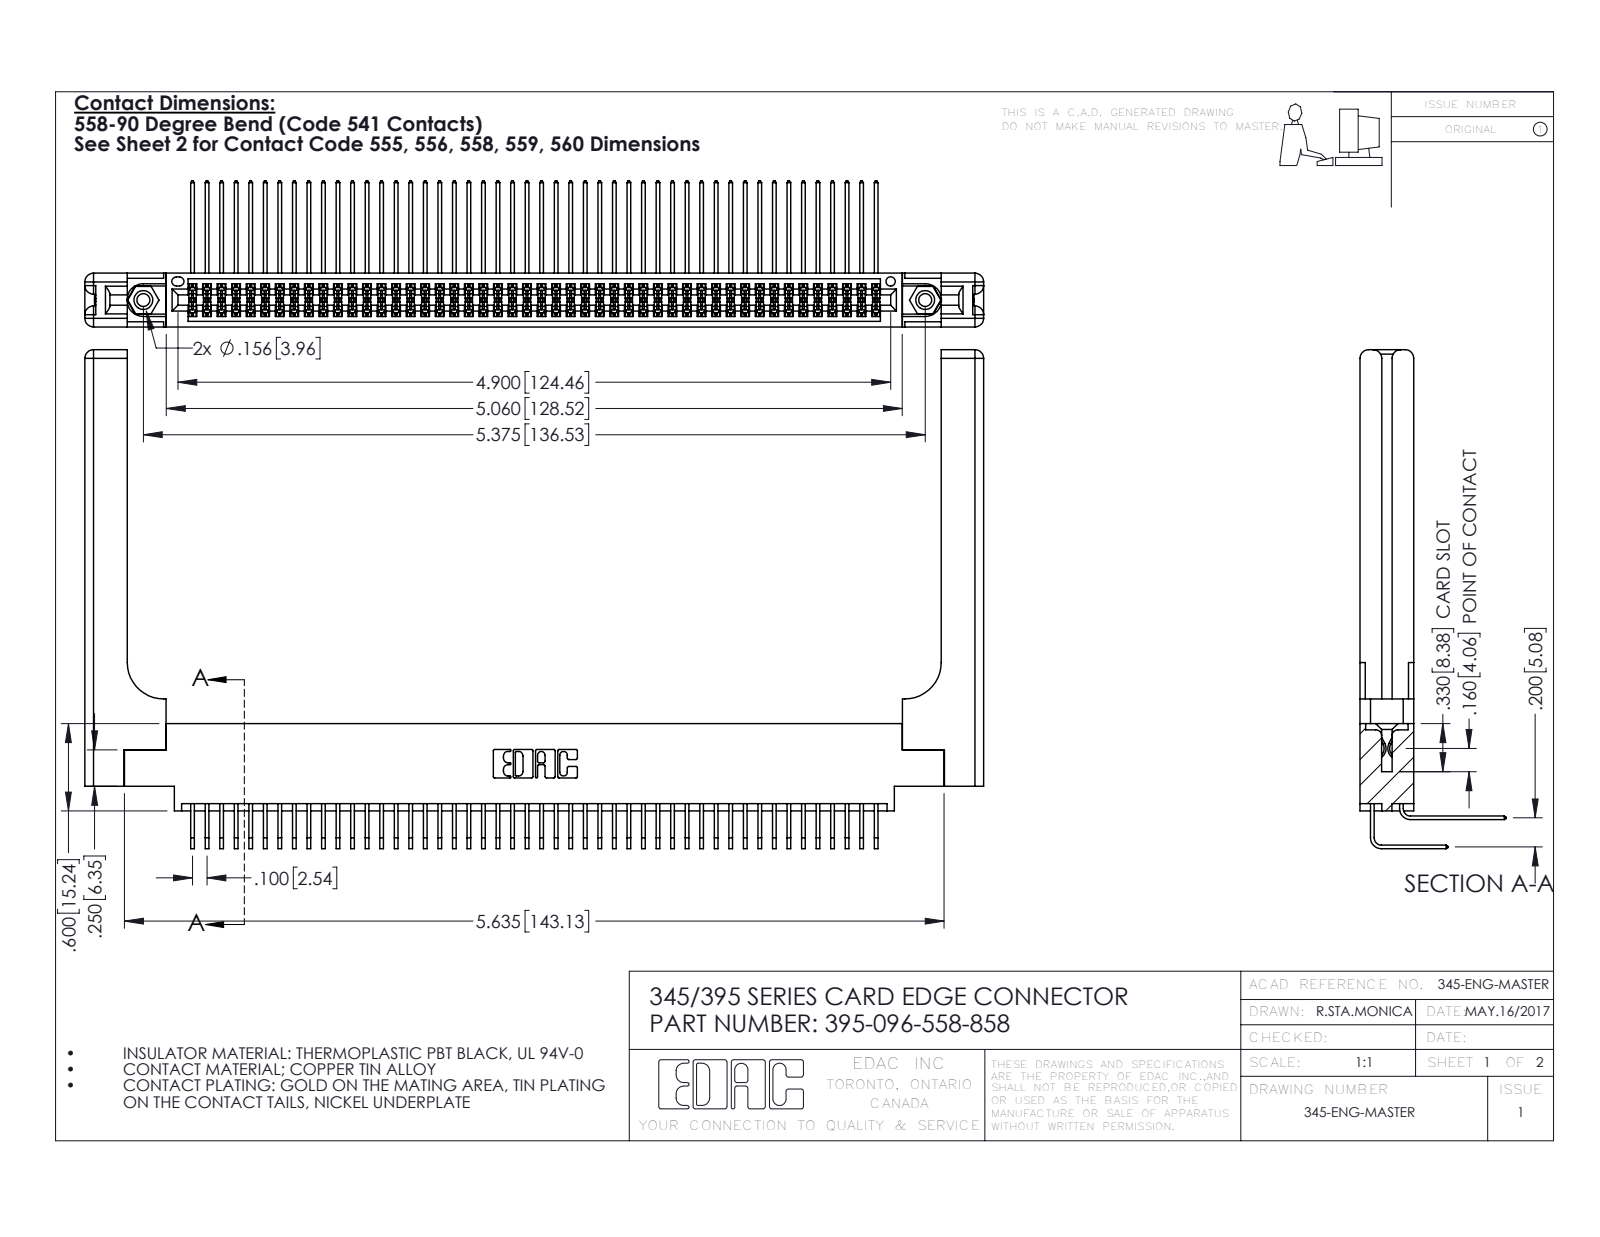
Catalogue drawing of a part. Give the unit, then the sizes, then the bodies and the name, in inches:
Units: inches
Overall size (bounding box): 6.179 × 3.429 × 1.005
Round holes (diameter × count): ⌀0.089 ×2, ⌀0.125 ×2, ⌀0.156 ×2, ⌀0.064 ×1
Round bosses / shafts (diameter × count): ⌀0.155 ×2
Partial cylindrical surfaces — rounded edges, fillets, slot ends (radius × count): R0.006 ×145, R0.01 ×22, R0.06 ×16, R0.007 ×6, R0.031 ×6, R0.026 ×3, R0.014 ×2, R0.019 ×2
Main face-to-face distances: 0.072, 0.37, 0.298, 0.2, 0.098, 0.272, 0.025, 0.225, 0.148, 0.15
Hole centre spacings: 0.27, 5.139, 5.375
Volume: 1.478 in³ · Surface area: 48.35 in²
Bodies: 101 solids, 5378 faces (3592 planar, 1726 cylindrical, 60 other)
Part name (STEP PRODUCT): 345-250-001_345-250-001-102; 395-096-558-858; 345 Part_0.170 Offset - 0.156 Dia-TH; 345-220-058_345-220-058 (+2 more)
STEP written by: SolidWorks 2016 (CONFIG_CONTROL_DESIGN)
